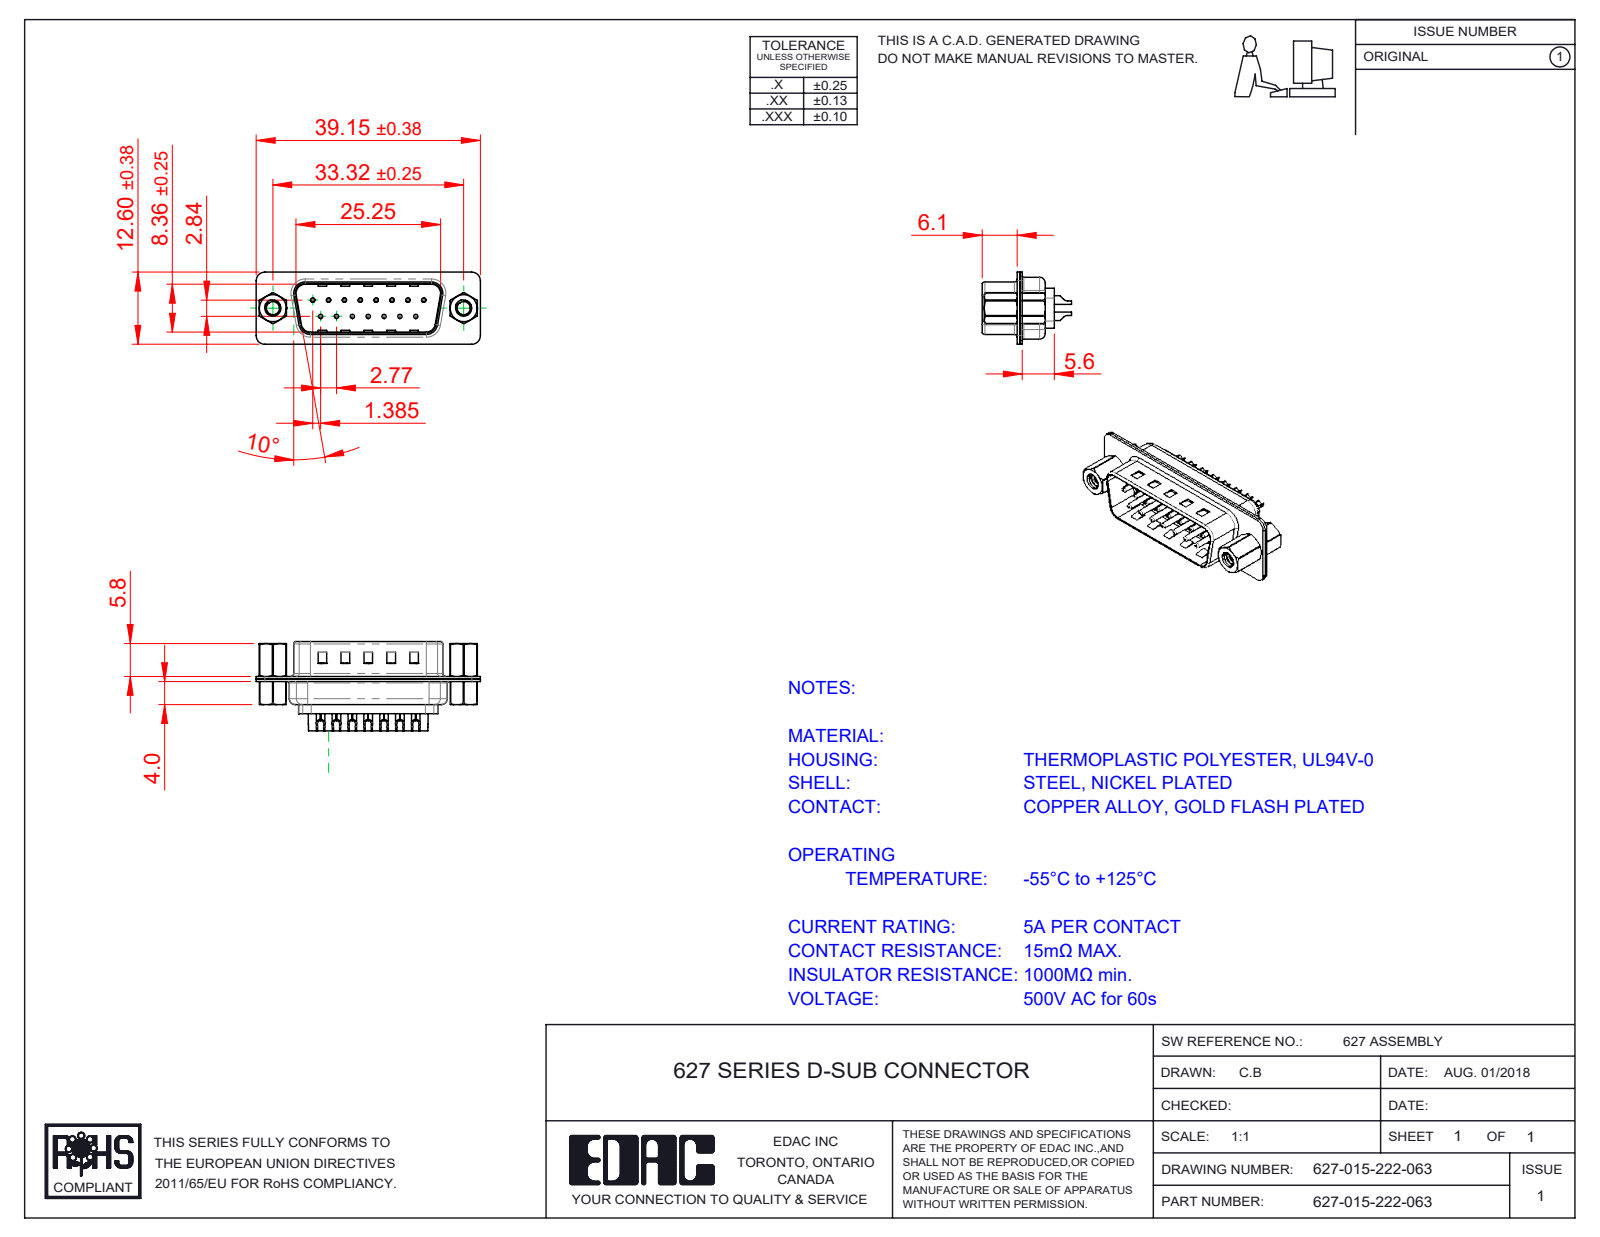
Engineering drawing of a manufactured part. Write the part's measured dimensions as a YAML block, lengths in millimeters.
part_name: "627 4-40 Hex Standoff; 627 4-40 Threaded Rivet; 627 Housing_15 LP; 627-015-222-063 (+4 more)"
step_written_by: "SolidWorks 2020 (CONFIG_CONTROL_DESIGN)"
units: millimeters
bodies: {solids: 22, faces: 1422, planar: 371, cylindrical: 638, other: 413}
overall_size: [39.15, 15.35, 12.6]
volume: 2043
surface_area: 5895
round_holes:
  - {diameter: 0.35, count: 15}
  - {diameter: 1.1, count: 15}
  - {diameter: 1.6, count: 15}
  - {diameter: 2.26, count: 2}
  - {diameter: 2.29, count: 2}
  - {diameter: 4, count: 2}
  - {diameter: 4.8, count: 2}
round_bosses_or_shafts:
  - {diameter: 2, count: 15}
  - {diameter: 1.5, count: 15}
  - {diameter: 0.75, count: 15}
  - {diameter: 5, count: 2}
  - {diameter: 4.9, count: 2}
  - {diameter: 2.79, count: 2}
partial_cylinders:
  - {radius: 1.5, count: 16}
  - {radius: 2, count: 12}
  - {radius: 0.5, count: 8}
  - {radius: 1.6, count: 8}
  - {radius: 1, count: 6}
  - {radius: 0.25, count: 4}
  - {radius: 0.6, count: 4}
  - {radius: 0.65, count: 4}
face_to_face_distances: [0.4, 0.45, 0.9, 0.82, 9.58, 8.76, 1.5, 1.4, 6.5, 5.6]
hole_center_spacings: [3.16, 2.77, 5.54, 8.31, 11.08, 5.03, 5.04, 7.48]
